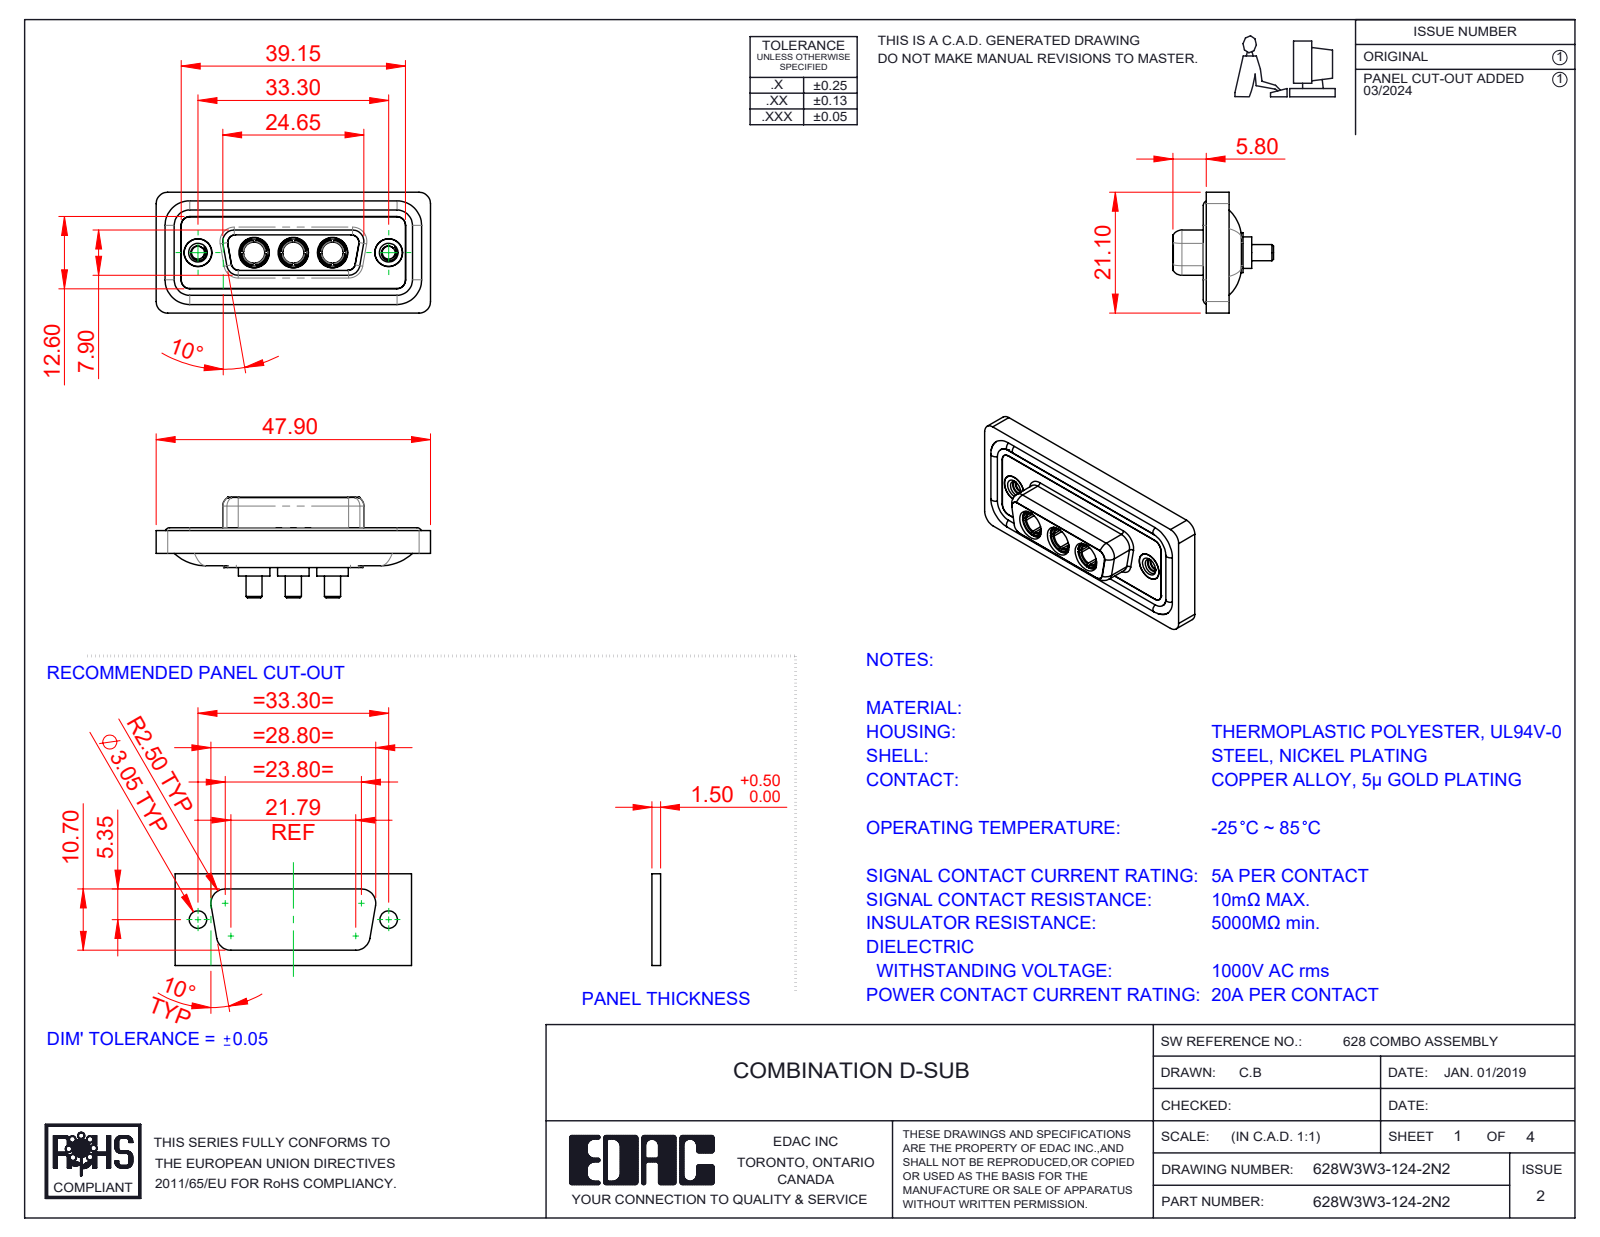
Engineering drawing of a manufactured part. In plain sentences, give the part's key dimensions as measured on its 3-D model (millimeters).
The part is named "628Combo Housing_3W3; 628Combo Threaded Rivet_2; 628Combo Shell Front_15 Contacts; Power Socket_20A S (+3 more)". Its 3-D file was written by "SolidWorks 2023 (CONFIG_CONTROL_DESIGN)". It is 13 solids with 608 faces: 192 planar, 257 cylindrical and 159 other. Overall it measures 47.9 by 21.1 by 17.55 millimeters. Its volume is 6 026 cubic millimeters and its surface area 9 739 square millimeters. Round holes: 5 of diameter 4.85, 3 of diameter 3.7, 3 of diameter 5.3, 2 of diameter 2.26, 2 of diameter 4, 2 of diameter 4.05, 2 of diameter 5. Round bosses or shafts: 4 of diameter 1.6, 3 of diameter 5.5, 3 of diameter 5.2, 3 of diameter 4.96, 3 of diameter 4.75, 3 of diameter 3.75, 3 of diameter 2.8, 2 of diameter 4.95. Partial cylindrical surfaces (rounded edges, fillets, slot ends): 22 of radius 1.5, 20 of radius 2, 12 of radius 1.35, 8 of radius 1.6, 4 of radius 0.25, 4 of radius 0.5, 4 of radius 0.6, 4 of radius 0.65. The main face-to-face distances are 0.4, 1.8, 1.6, 0.5, 7.45, 1.1, 2.9, 5.65, 7.05, 6.6. The hole center spacings are 6.85, 9.8, 16.65, 23.5, 13.7, 33.3.
